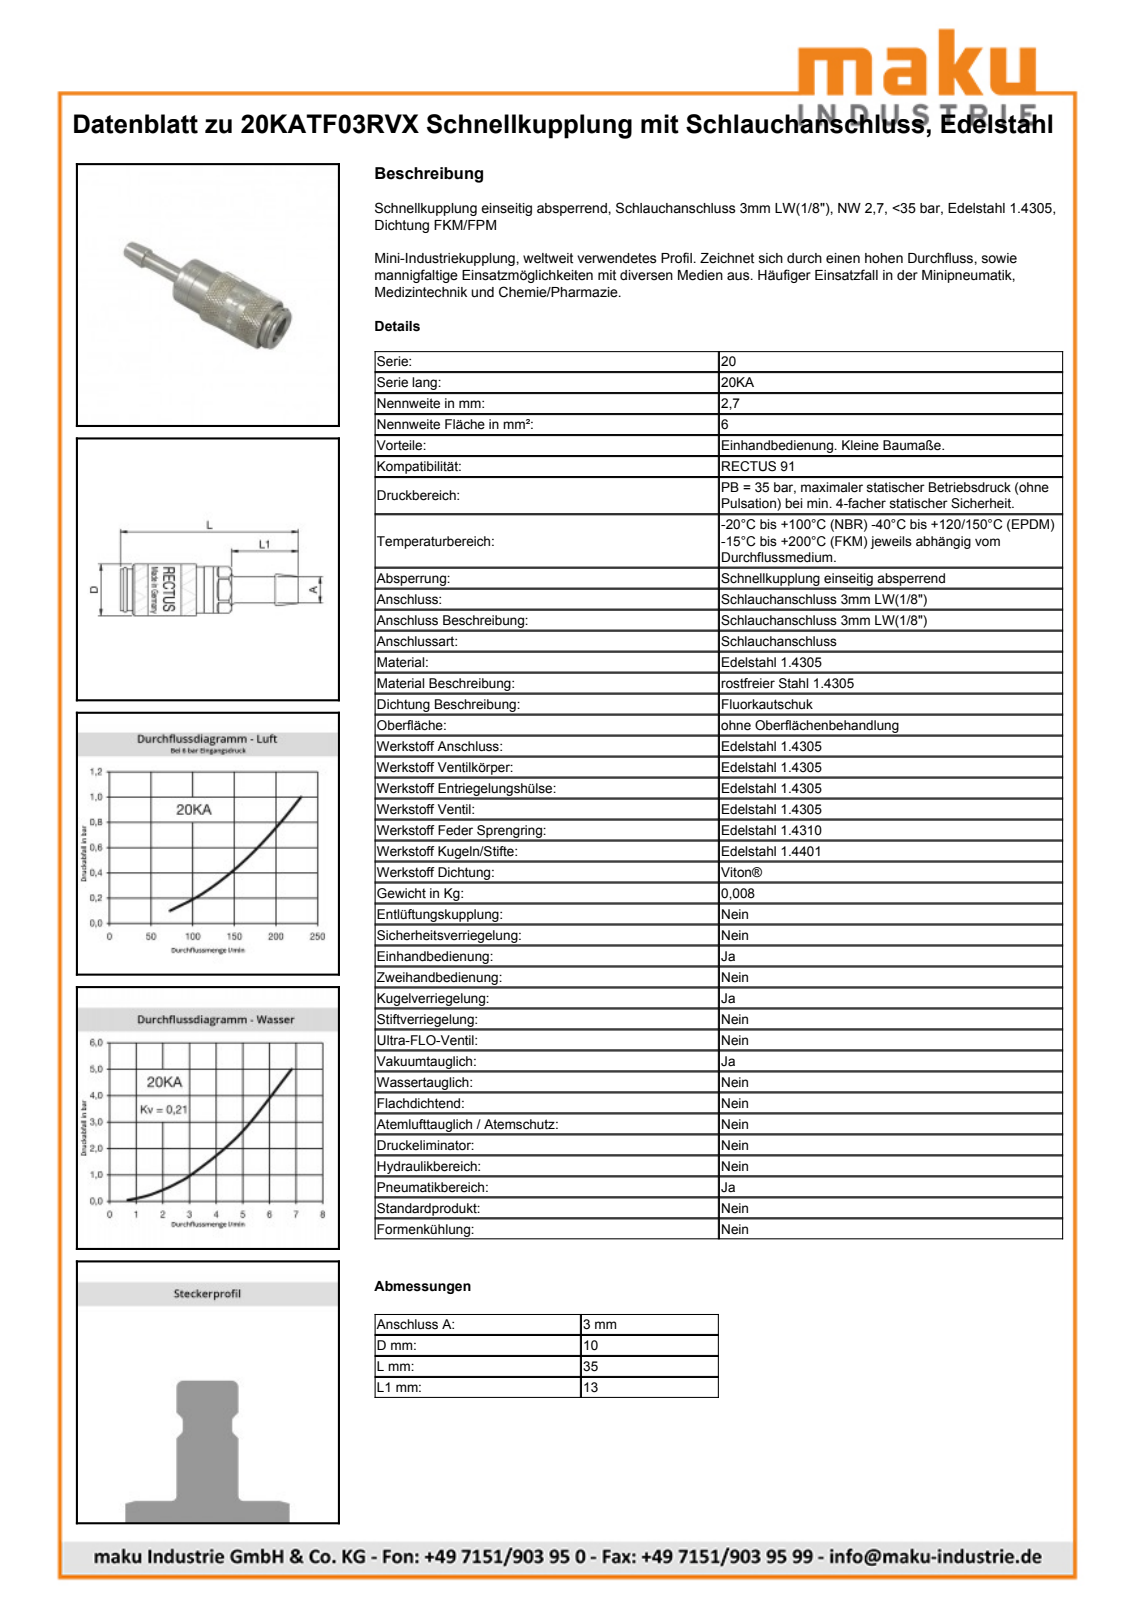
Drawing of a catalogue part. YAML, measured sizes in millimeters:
part_name: "D104279"
step_written_by: "Autodesk Inventor 2011 (AUTOMOTIVE_DESIGN)"
units: millimeters
bodies: {solids: 2, faces: 441, planar: 170, cylindrical: 59, other: 212}
overall_size: [34.55, 10.35, 10.35]
volume: 1501
surface_area: 1873
round_holes:
  - {diameter: 7.46, count: 1}
  - {diameter: 8.1, count: 1}
  - {diameter: 8.15, count: 1}
  - {diameter: 9.15, count: 1}
  - {diameter: 9.2, count: 1}
round_bosses_or_shafts:
  - {diameter: 10.35, count: 1}
  - {diameter: 10, count: 1}
  - {diameter: 9.8, count: 1}
  - {diameter: 9, count: 1}
  - {diameter: 8.9, count: 1}
  - {diameter: 8, count: 1}
  - {diameter: 7.8, count: 1}
  - {diameter: 7.4, count: 1}
partial_cylinders:
  - {radius: 3.38, count: 1}
face_to_face_distances: [21.55, 8, 3.2, 2.5, 19.05, 5, 18, 15.5, 3.55, 14.8]
